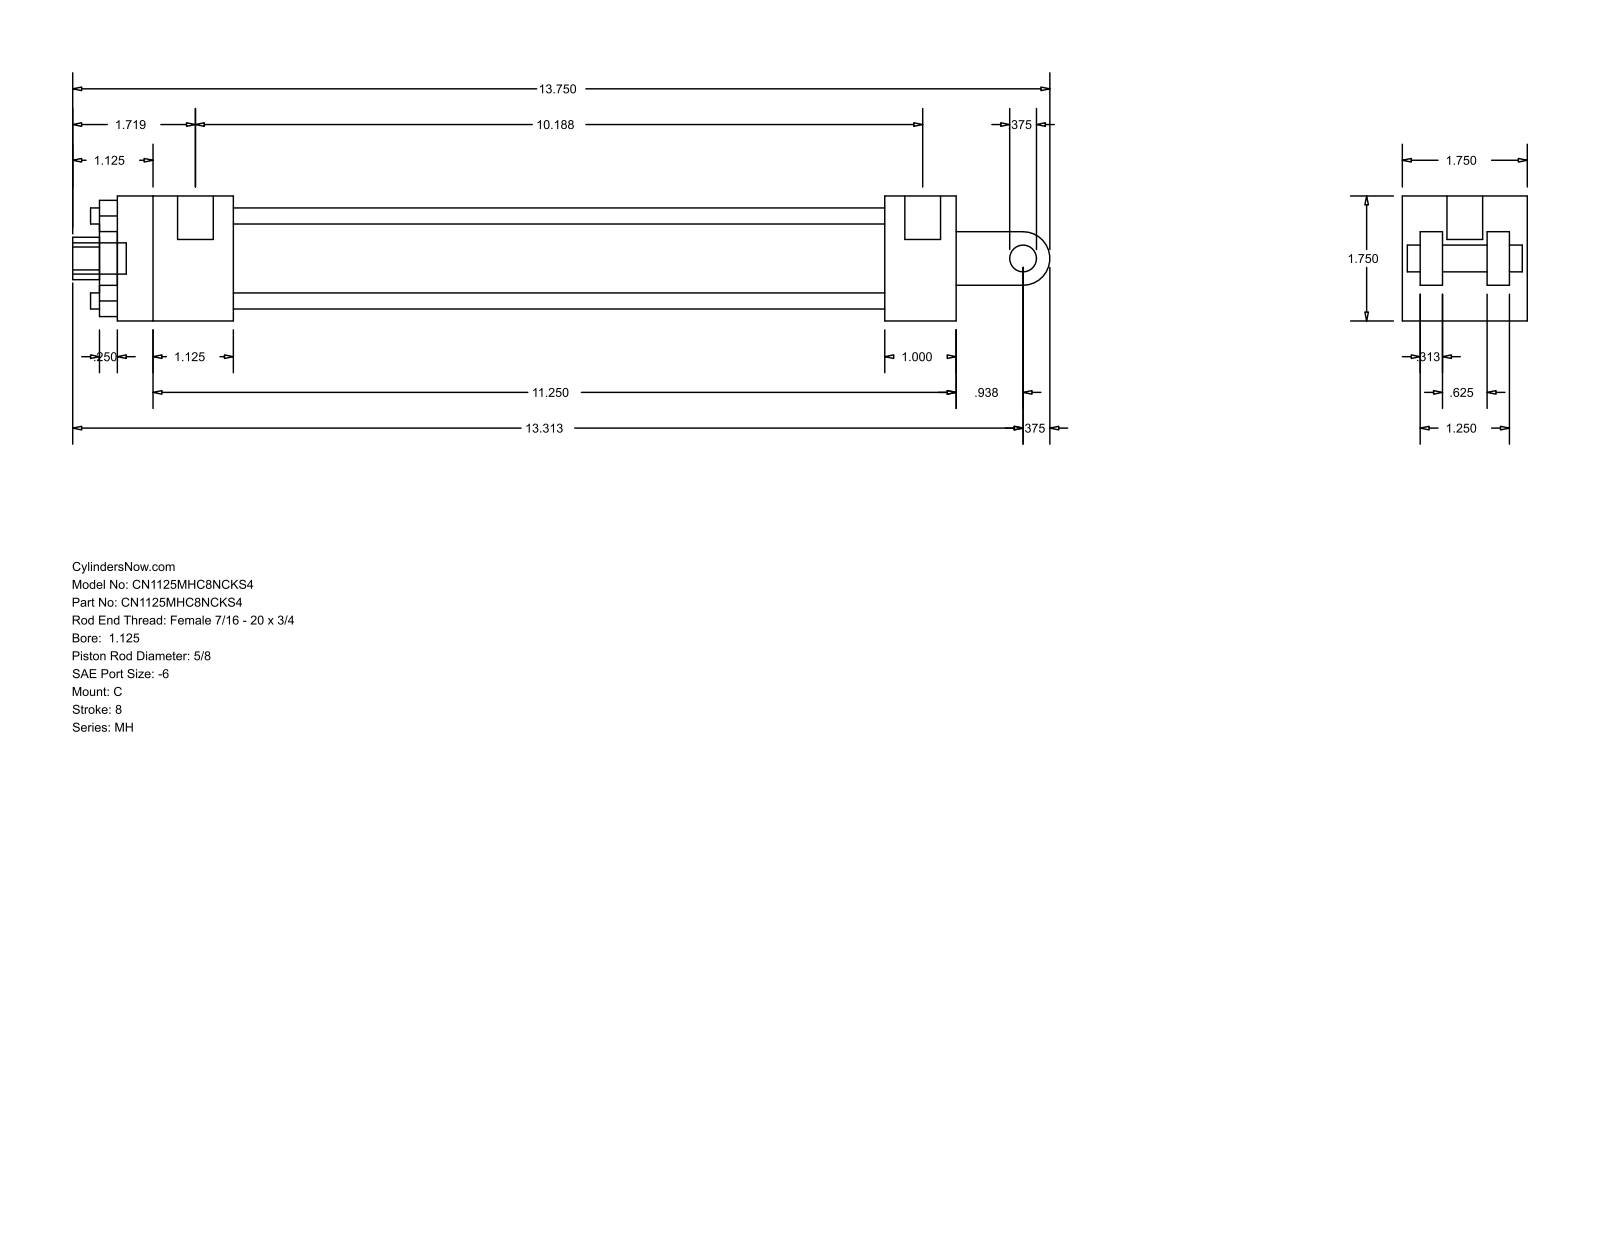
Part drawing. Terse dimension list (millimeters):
name: MH_C__0112_0.625
written by: GSSL Pune (CONFIG_CONTROL_DESIGN)
unit: mm
bodies: 0 solids, 99 faces (70 planar, 29 cylindrical, 0 other)
size: 347.66 × 44.45 × 44.45
holes: 4× ⌀5.71, 2× ⌀5.56, 1× ⌀12.7, 1× ⌀15.88, 1× ⌀28.57, 1× ⌀34.92
bosses: 2× ⌀5.56, 1× ⌀12.7, 1× ⌀11.11, 1× ⌀9.53
rounds: 1× R7.54, 1× R9.53
face distances: 44.46, 6.35, 31.76, 14.29, 12.7, 30.17, 38.11, 7.94, 23.82, 41.27
hole spacings: 21.37, 30.22, 42.74
